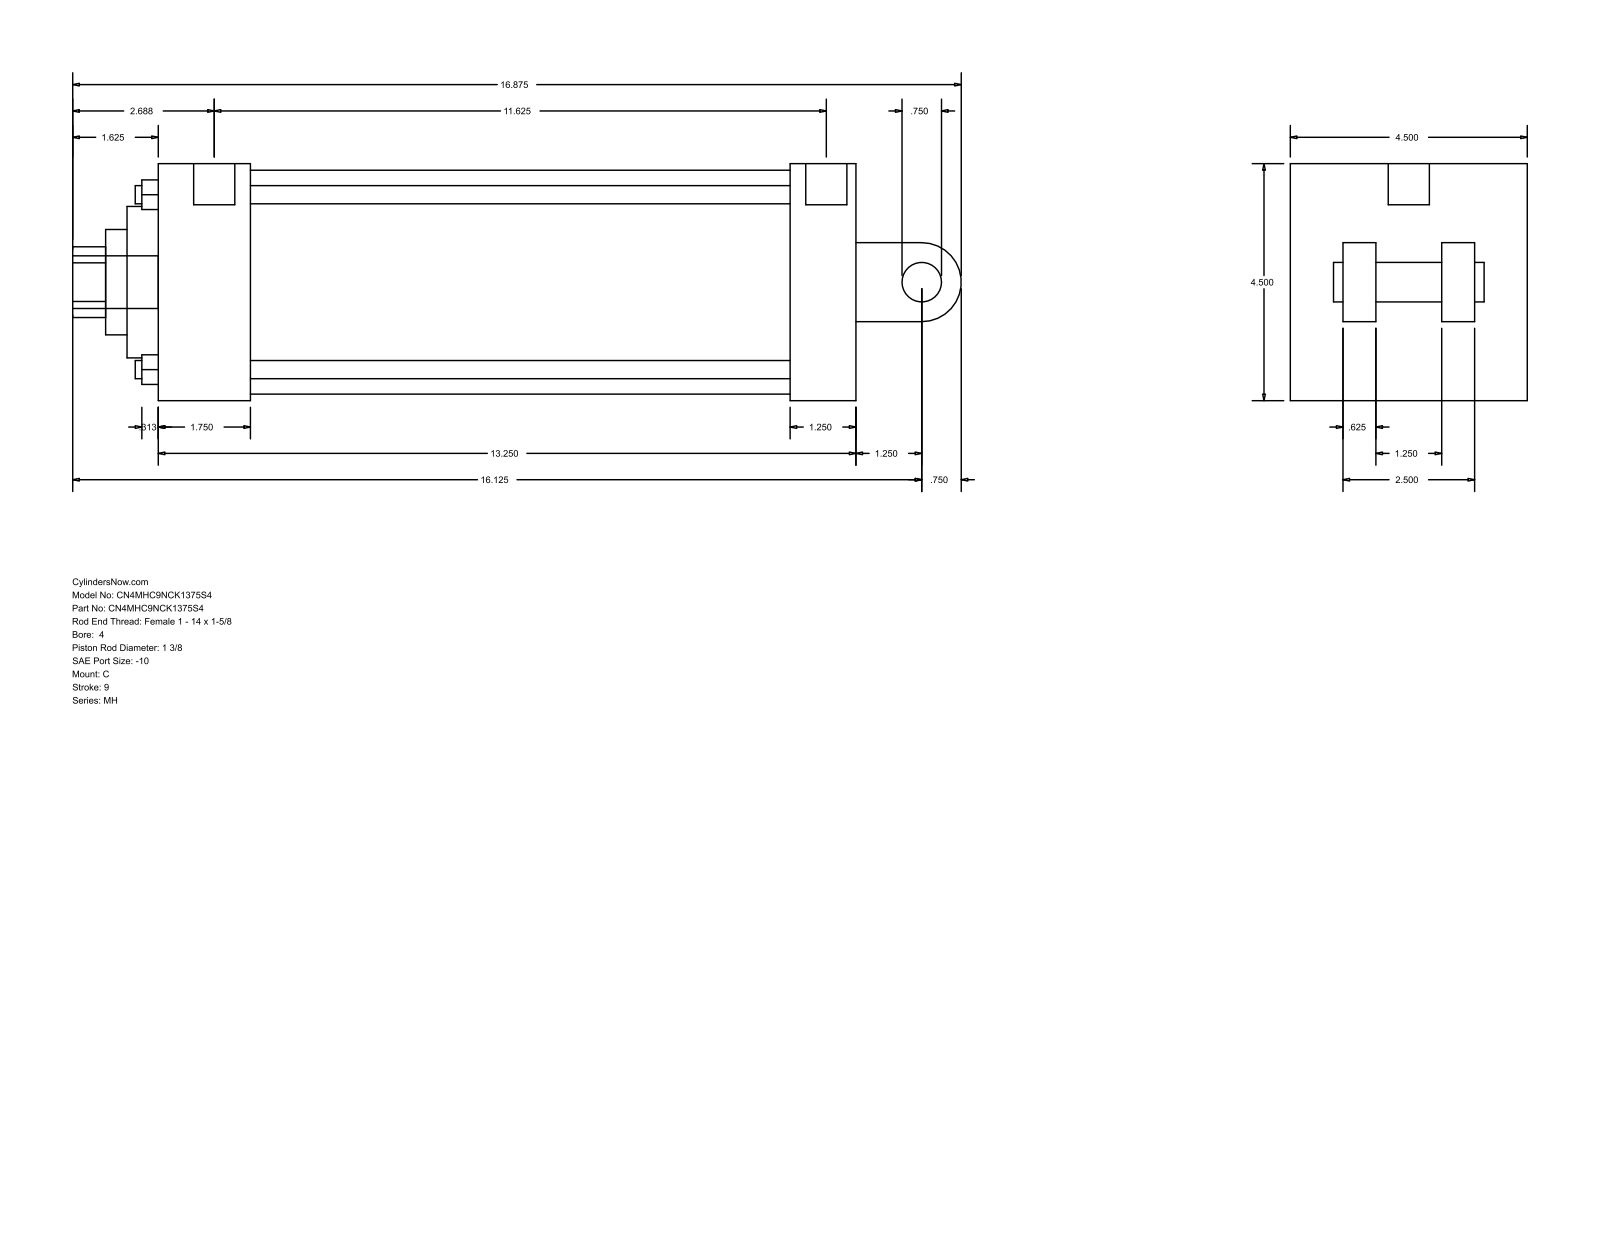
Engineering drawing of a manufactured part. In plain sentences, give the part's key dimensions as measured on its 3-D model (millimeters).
The part is named "MH_C__0400_1.375". Its 3-D file was written by "GSSL Pune (CONFIG_CONTROL_DESIGN)". It is 0 solids with 101 faces: 71 planar, 30 cylindrical and 0 other. Overall it measures 428.62 by 114.3 by 114.3 millimeters. Round holes: 4 of diameter 8.76, 2 of diameter 8.73, 1 of diameter 19.84, 1 of diameter 34.92, 1 of diameter 50.8, 1 of diameter 73.03, 1 of diameter 107.95. Round bosses or shafts: 2 of diameter 8.73, 1 of diameter 25.4, 1 of diameter 19.84, 1 of diameter 19.05. Partial cylindrical surfaces (rounded edges, fillets, slot ends): 1 of radius 17.06, 1 of radius 19.05. The main face-to-face distances are 114.3, 336.55, 44.45, 304.8, 260.35, 292.1, 31.75, 73.03, 41.27, 38.1. The hole center spacings are 59.62, 84.32, 119.25, 1.58.
